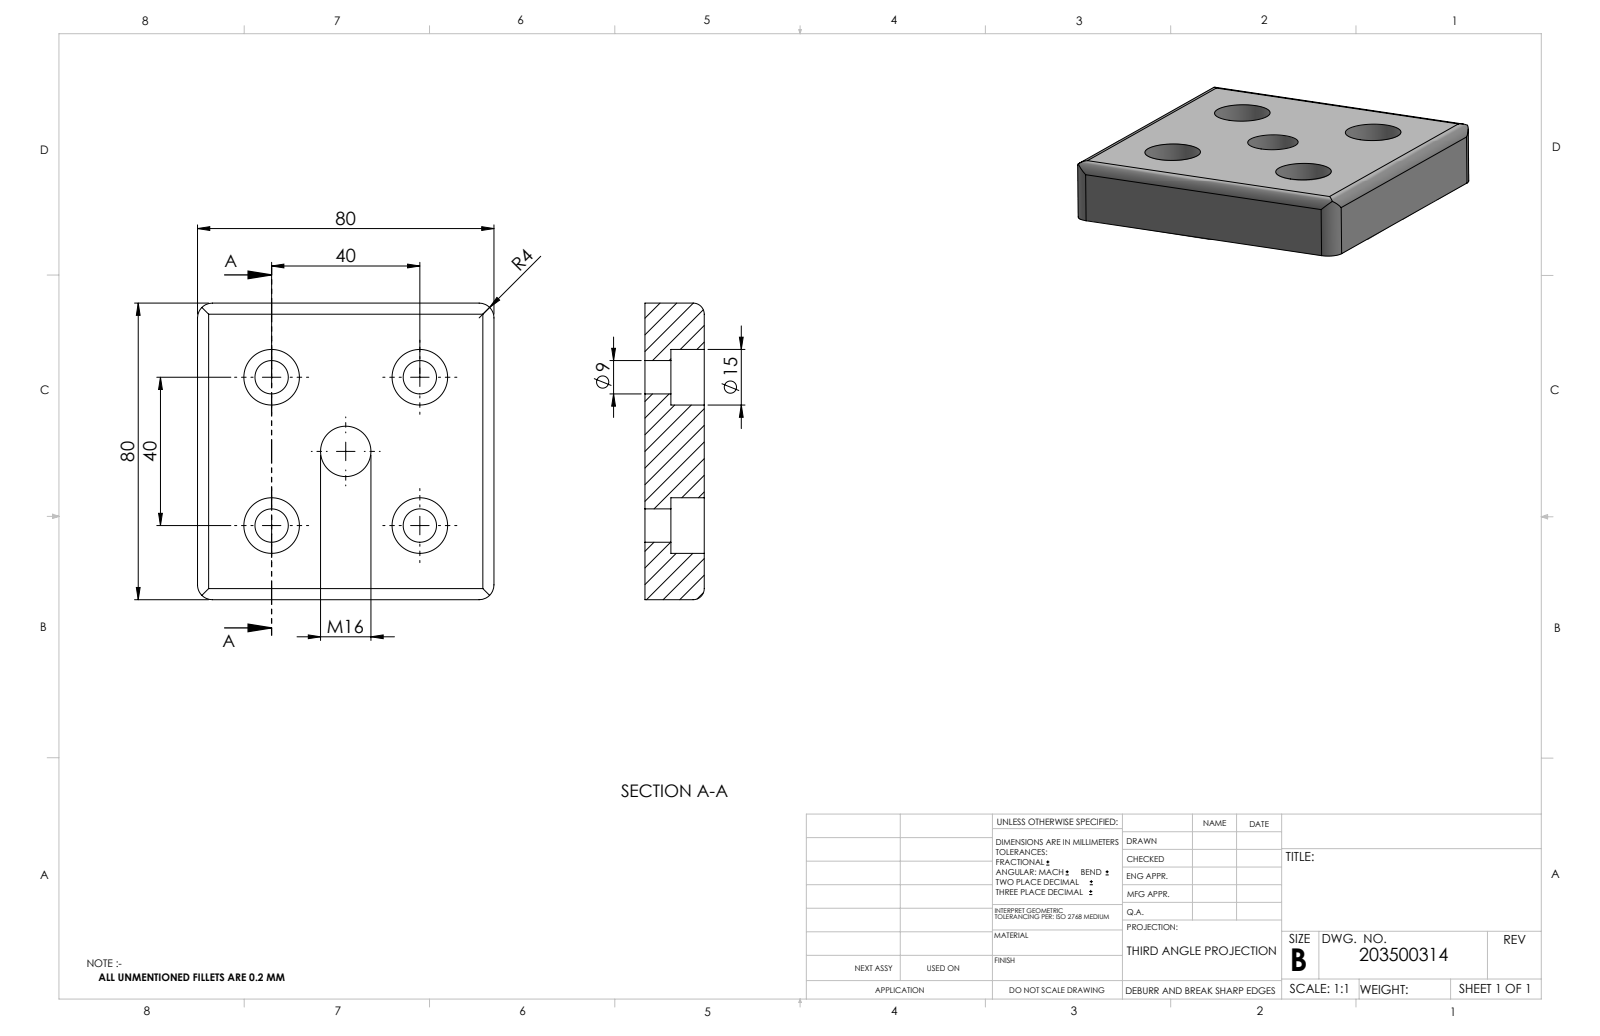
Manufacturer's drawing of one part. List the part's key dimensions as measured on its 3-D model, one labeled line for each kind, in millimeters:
Part name (STEP PRODUCT): 203500314_c_1
STEP written by: SolidWorks 2014 (CONFIG_CONTROL_DESIGN)
Units: millimetres
Bodies: 1 solid, 36 faces (10 planar, 26 cylindrical, 0 other)
Overall size (bounding box): 80 × 80 × 16
Volume: 91 129 mm³ · Surface area: 19 758 mm²
Round holes (diameter × count): ⌀9 ×4, ⌀15 ×4, ⌀13.6 ×1
Partial cylindrical surfaces — rounded edges, fillets, slot ends (radius × count): R3 ×4, R4 ×4
Main face-to-face distances: 16, 80, 7, 9
Hole centre spacings: 28.28, 40, 56.57
